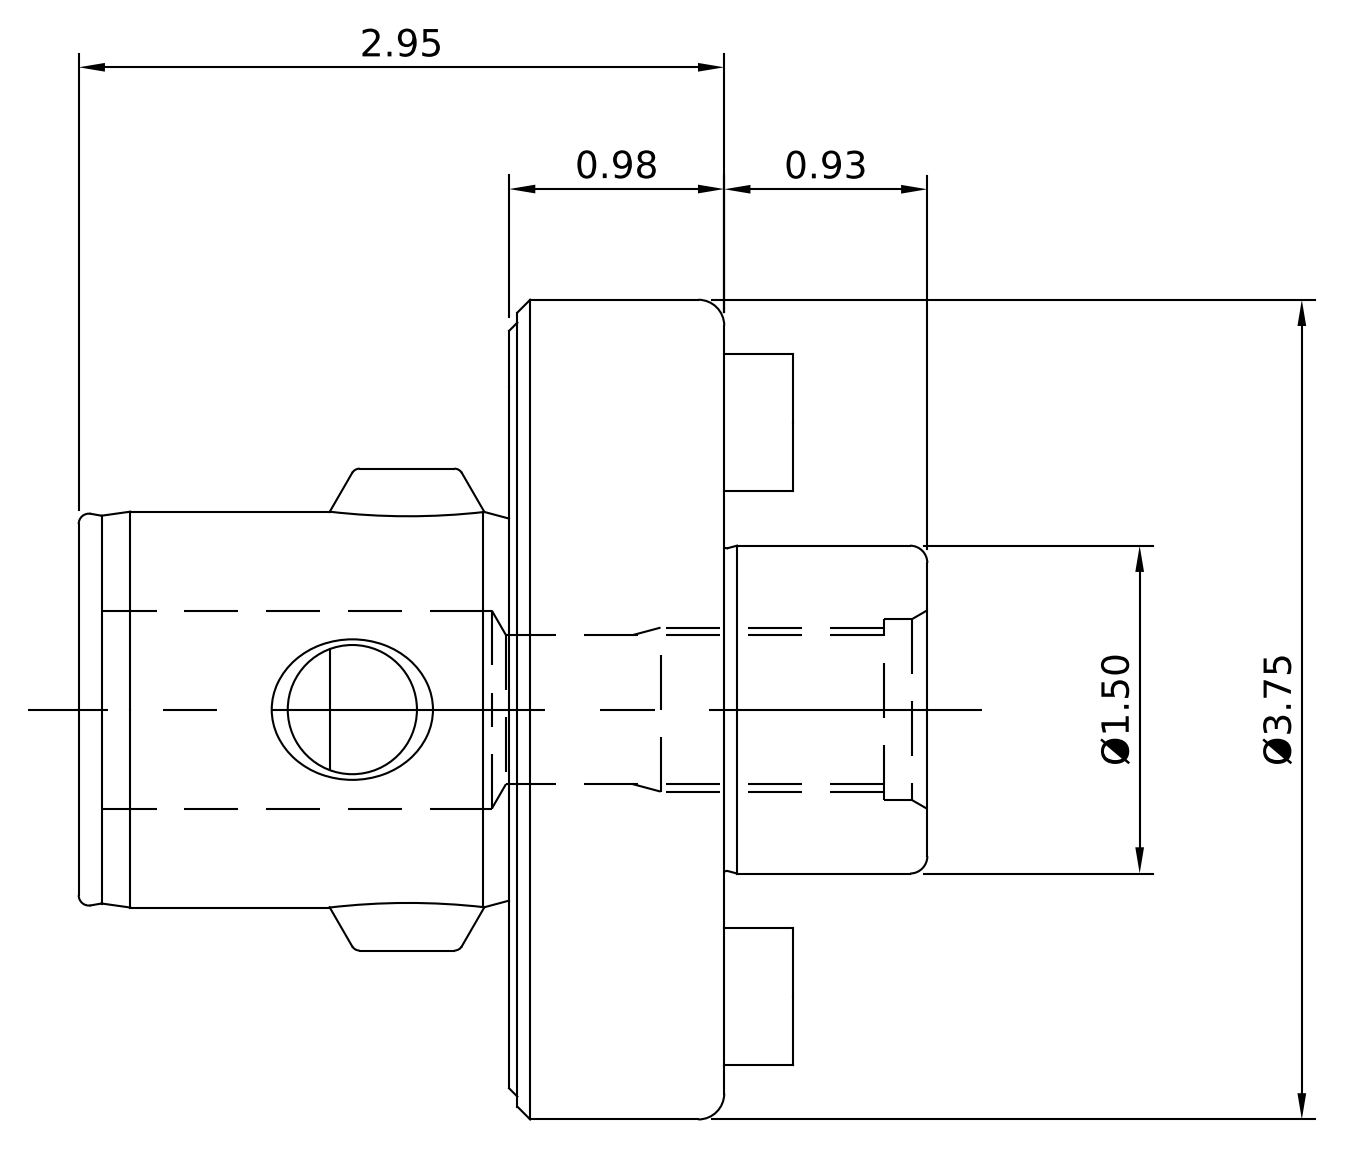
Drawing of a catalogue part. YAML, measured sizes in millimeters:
part_name: "11.335.415; 11.691.624; 11.690.713"
step_written_by: "SolidWorks 2010 (CONFIG_CONTROL_DESIGN)"
units: millimeters
bodies: {solids: 4, faces: 269, planar: 50, cylindrical: 89, other: 130}
overall_size: [111.3, 95.25, 95.25]
volume: 276452
surface_area: 50757
round_holes:
  - {diameter: 15.87, count: 2}
  - {diameter: 9.6, count: 1}
  - {diameter: 15, count: 1}
  - {diameter: 17.46, count: 1}
  - {diameter: 18, count: 1}
  - {diameter: 21, count: 1}
  - {diameter: 22, count: 1}
  - {diameter: 24.7, count: 1}
round_bosses_or_shafts:
  - {diameter: 15.88, count: 2}
  - {diameter: 95.25, count: 1}
  - {diameter: 47.62, count: 1}
  - {diameter: 46, count: 1}
  - {diameter: 38.1, count: 1}
  - {diameter: 19.05, count: 1}
partial_cylinders:
  - {radius: 23, count: 1}
face_to_face_distances: [25, 48.6, 23.6, 61.3, 36.3, 12.7, 50, 75, 98.6, 111.3]
hole_center_spacings: [33.34, 66.68]
